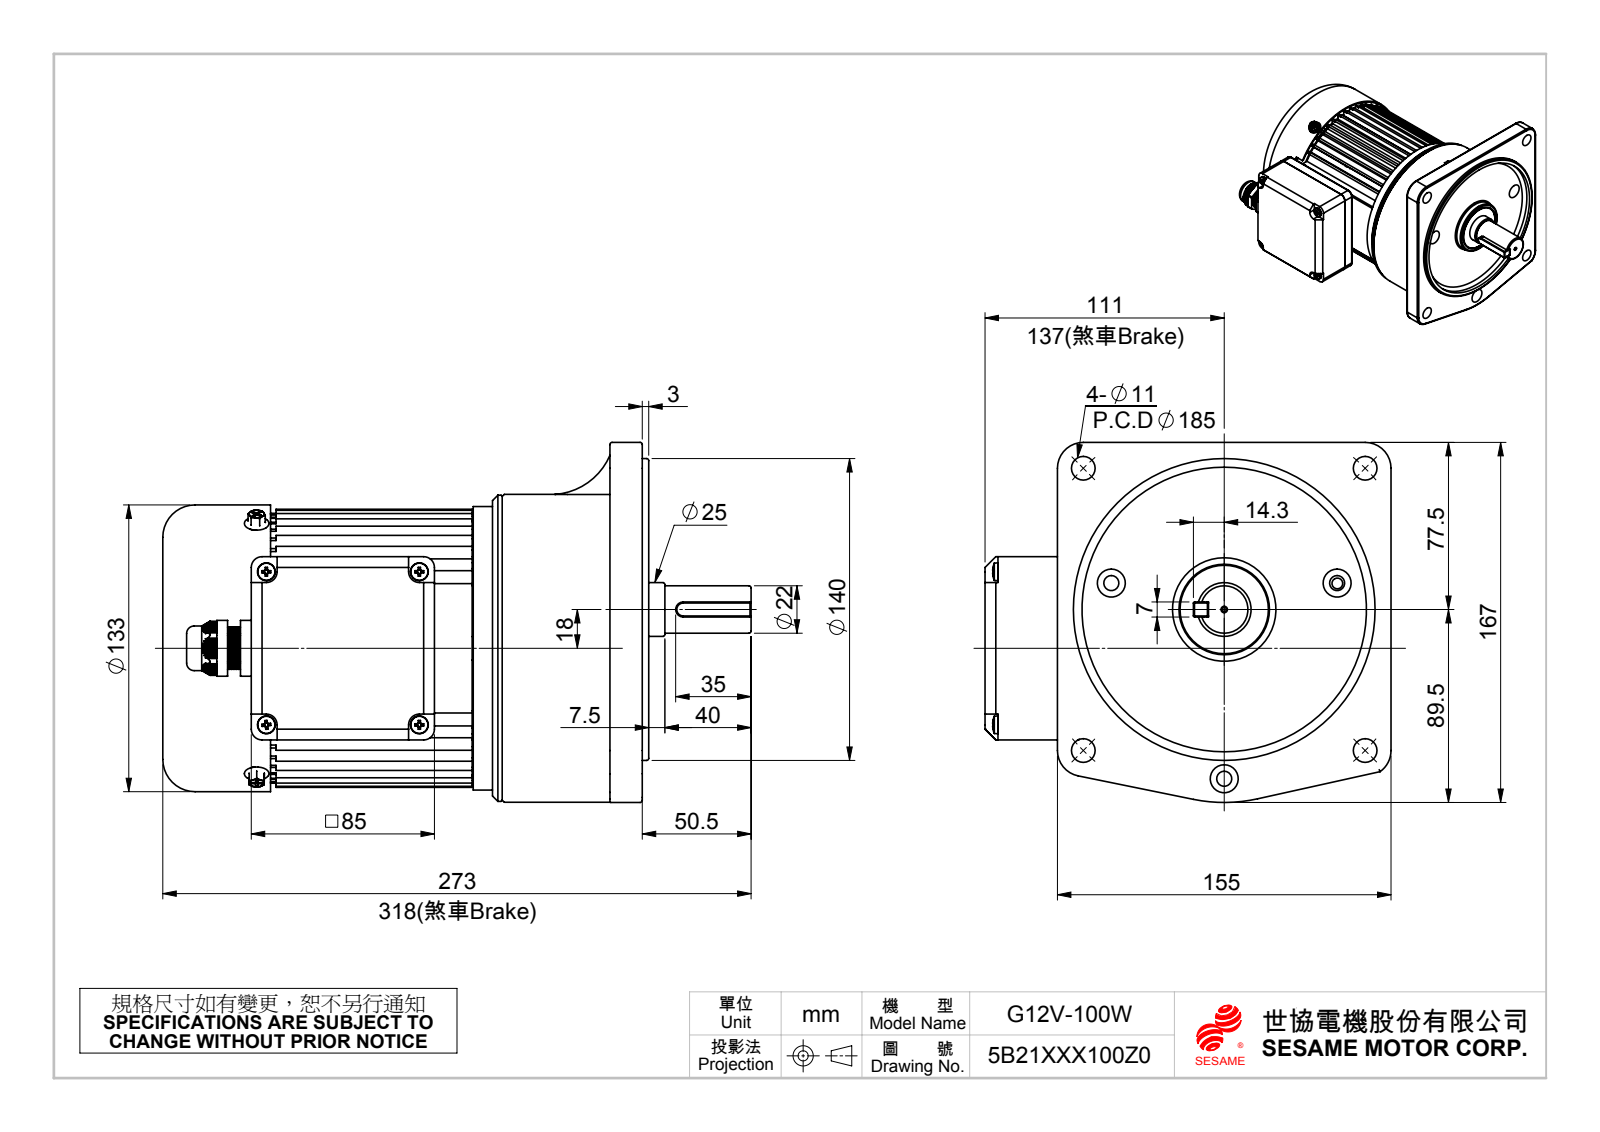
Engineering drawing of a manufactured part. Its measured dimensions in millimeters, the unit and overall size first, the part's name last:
Units: millimetres
Overall size (bounding box): 273 × 188.4 × 167
Round holes (diameter × count): ⌀5 ×14, ⌀3.3 ×9, ⌀11 ×7, ⌀8 ×4, ⌀4.2 ×3, ⌀7 ×3, ⌀13 ×3, ⌀2 ×1, ⌀7.5 ×1, ⌀10.8 ×1, ⌀16.5 ×1, ⌀24.95 ×1
Round bosses / shafts (diameter × count): ⌀8.3 ×4, ⌀4 ×4, ⌀5 ×3, ⌀142.8 ×1, ⌀142 ×1, ⌀140 ×1, ⌀133 ×1, ⌀131.5 ×1
Partial cylindrical surfaces — rounded edges, fillets, slot ends (radius × count): R1 ×101, R1.03 ×8, R2 ×8, R5 ×8, R2.75 ×6, R2.55 ×4, R3.55 ×4, R12 ×3
Main face-to-face distances: 2, 10, 18, 60, 18.95, 95, 113.95, 3, 105, 123.95
Hole centre spacings: 60.5, 104.79, 45, 71, 31.13, 11, 11.5, 14.66
Volume: 3 082 000 mm³ · Surface area: 412 728 mm²
Bodies: 19 solids, 2743 faces (815 planar, 881 cylindrical, 1047 other)
Part name (STEP PRODUCT): 100W風扇蓋131x50／缺口70(直角); 油封42x25x8; 7x7xL_35L; (標準品)G12V100W(5B21XXX100)(減速比共用) (+8 more)
STEP written by: SolidWorks 2010 (CONFIG_CONTROL_DESIGN)
